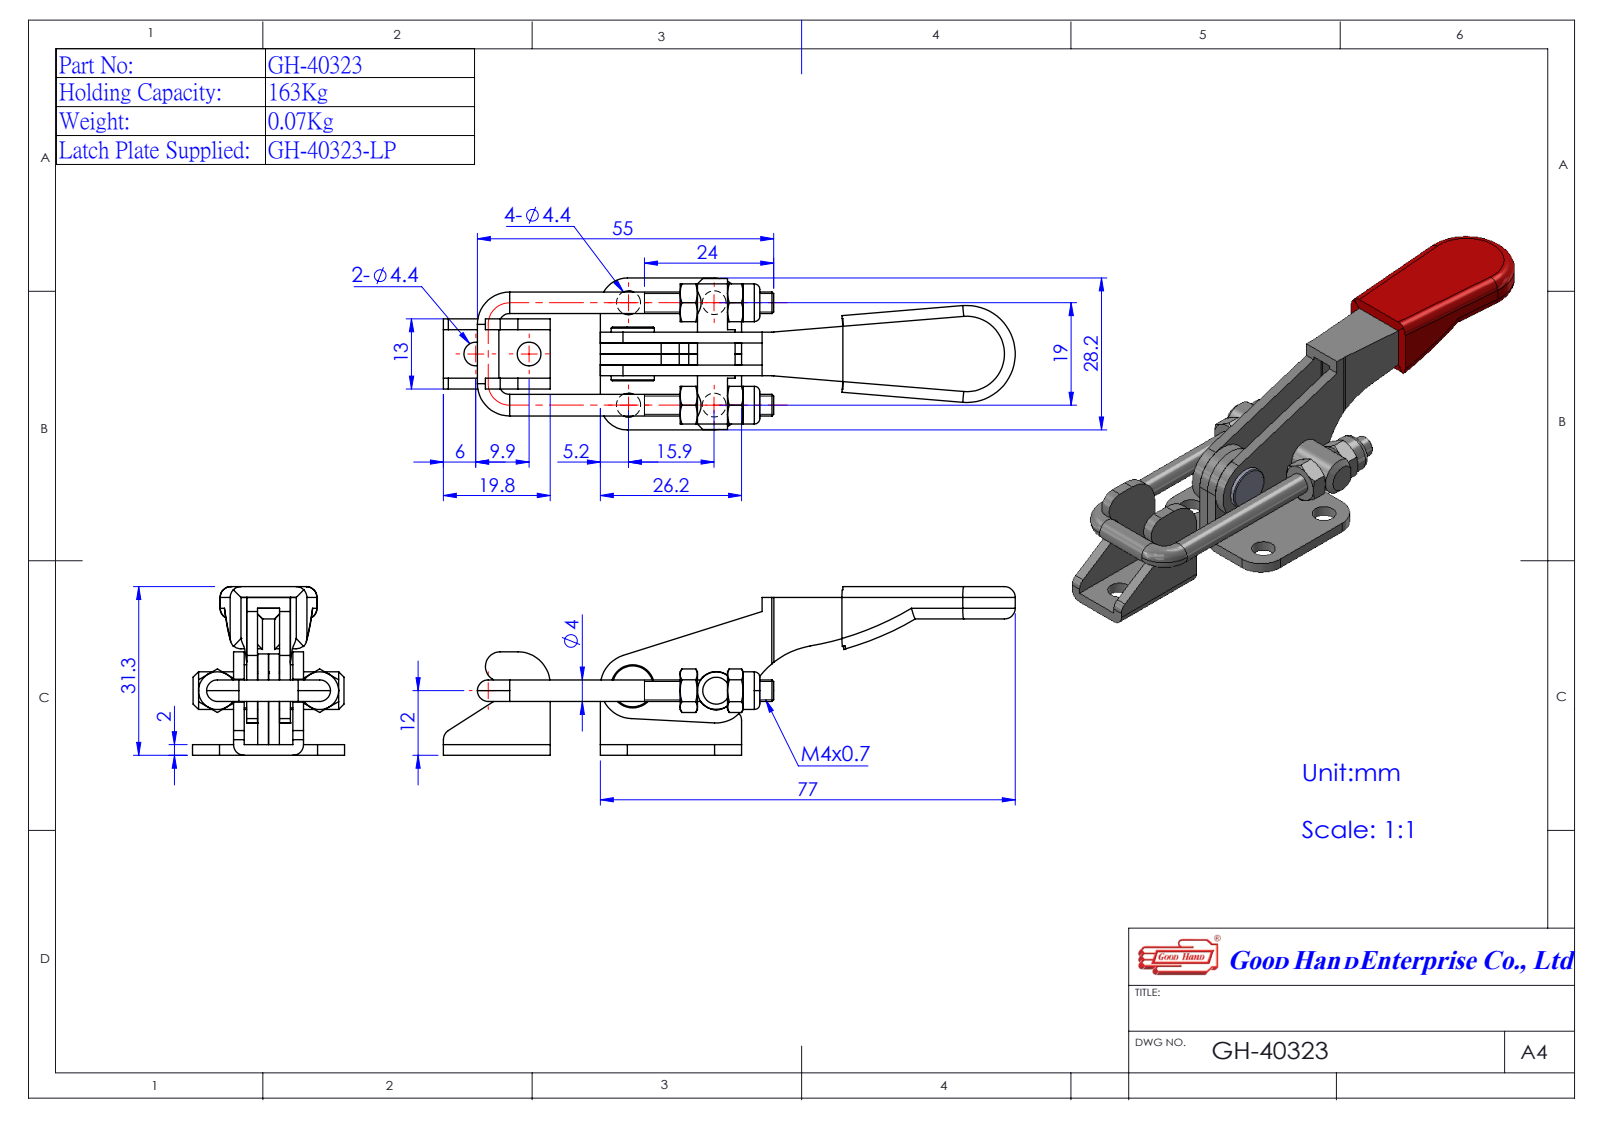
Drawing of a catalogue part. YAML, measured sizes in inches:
part_name: "493796(GH-40323); DEFAULT-7-1^493796(GH-40323); Group5^493796(GH-40323); Group4^493796(GH-40323) (+1 more)"
step_written_by: "SolidWorks 2016 (AUTOMOTIVE_DESIGN)"
units: inches
bodies: {solids: 8, faces: 290, planar: 118, cylindrical: 94, other: 78}
overall_size: [4.26, 1.232, 1.128]
volume: 0.778
surface_area: 21.03
round_holes:
  - {diameter: 0.173, count: 6}
  - {diameter: 0.13, count: 2}
  - {diameter: 0.191, count: 2}
  - {diameter: 0.118, count: 1}
  - {diameter: 0.276, count: 1}
round_bosses_or_shafts:
  - {diameter: 0.157, count: 3}
  - {diameter: 0.276, count: 2}
  - {diameter: 0.315, count: 1}
partial_cylinders:
  - {radius: 0.197, count: 6}
  - {radius: 0.079, count: 3}
  - {radius: 0.236, count: 3}
  - {radius: 0.098, count: 1}
  - {radius: 0.108, count: 1}
  - {radius: 0.276, count: 1}
  - {radius: 0.276, count: 1}
  - {radius: 0.354, count: 1}
face_to_face_distances: [0.079, 0.157, 0.078, 1.154, 0.096, 0.337, 1.075, 0.079, 0.24, 0.158]
hole_center_spacings: [0.748, 0.626, 0.89, 0.976, 1.254, 1.481, 1.861, 0.39]
